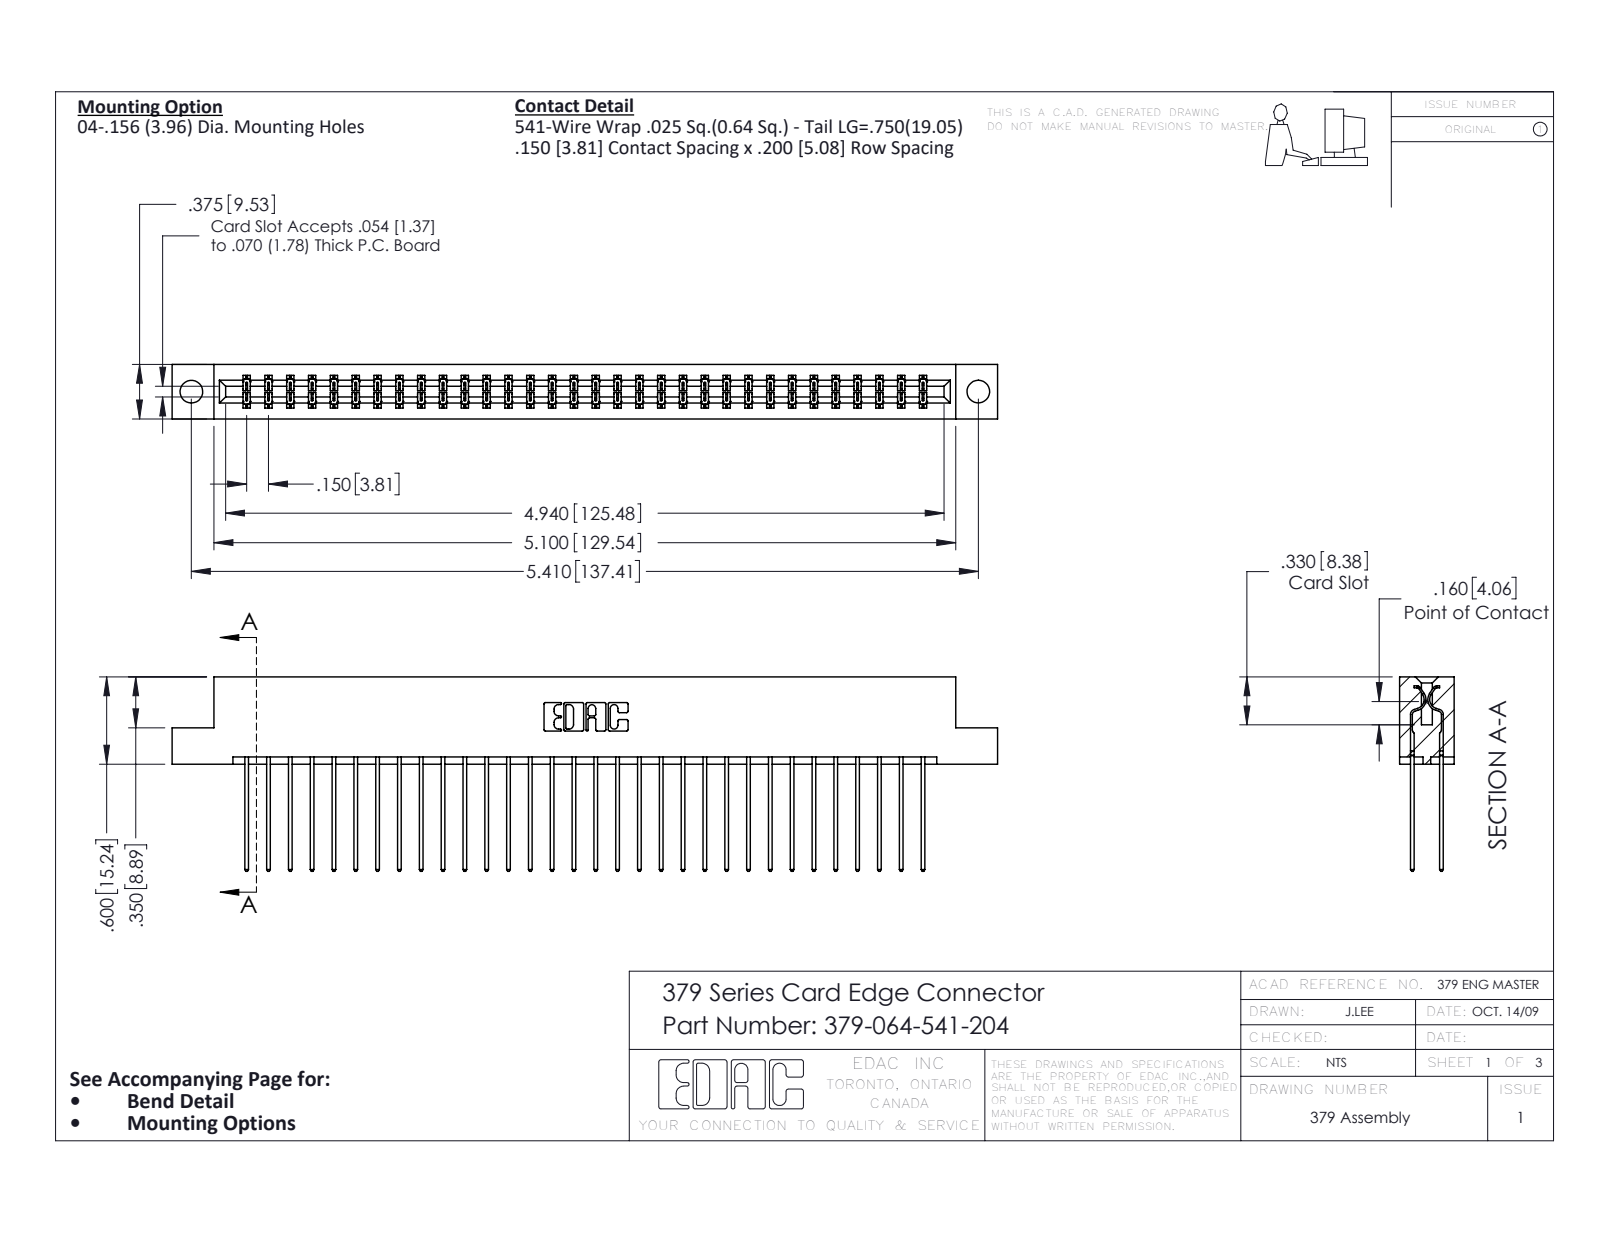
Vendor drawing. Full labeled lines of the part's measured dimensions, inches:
Part name (STEP PRODUCT): 345-292-001_345-293-141; 379 Part_Flush - .156 Dia - TH; 379-064-541-204
STEP written by: SolidWorks 2016 (CONFIG_CONTROL_DESIGN)
Units: inches
Bodies: 65 solids, 3442 faces (2374 planar, 1068 cylindrical, 0 other)
Overall size (bounding box): 5.675 × 1.337 × 0.375
Volume: 0.947 in³ · Surface area: 29.41 in²
Round holes (diameter × count): ⌀0.156 ×2
Partial cylindrical surfaces — rounded edges, fillets, slot ends (radius × count): R0.006 ×96, R0.01 ×64, R0.01 ×22, R0.007 ×6, R0.031 ×6, R0.026 ×3, R0.014 ×2, R0.022 ×2
Main face-to-face distances: 0.3, 0.075, 0.1, 0.375, 0.2, 0.275, 0.025, 0.076, 0.15, 0.225
Hole centre spacings: 5.41
